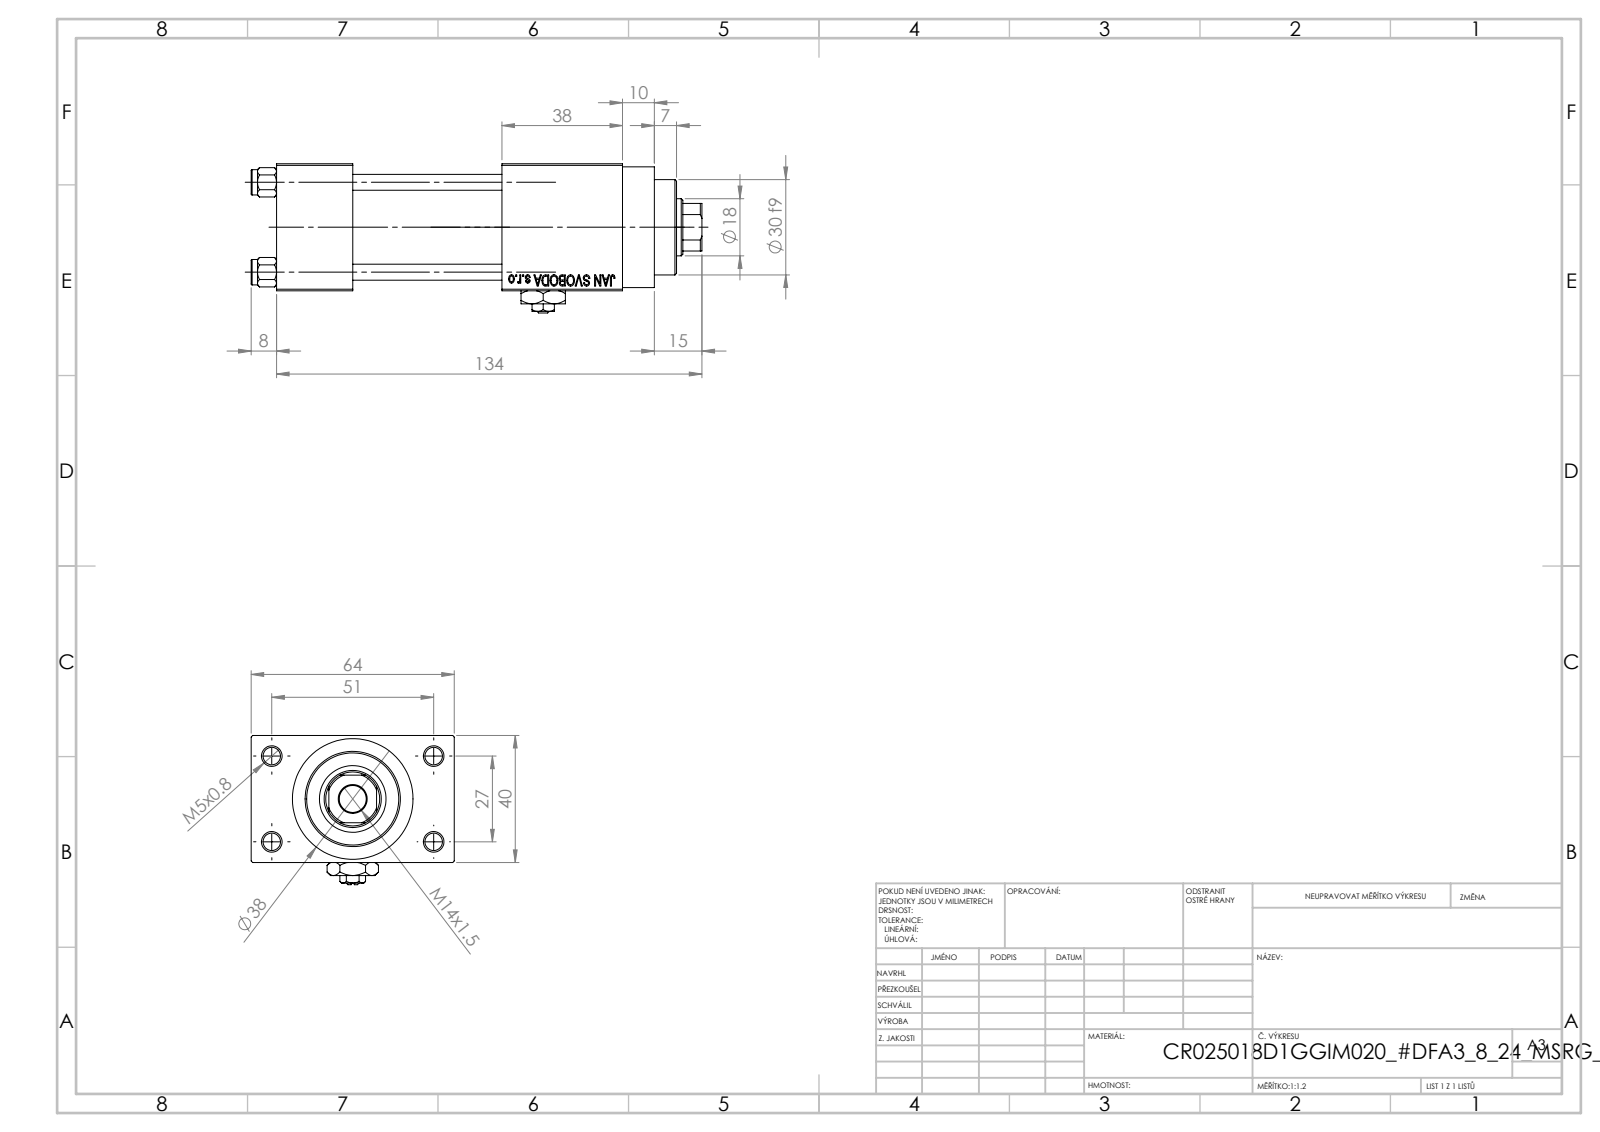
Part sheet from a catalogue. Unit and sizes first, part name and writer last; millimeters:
Units: millimetres
Overall size (bounding box): 142 × 64 × 47
Round holes (diameter × count): ⌀5 ×4, ⌀5.5 ×4, ⌀20 ×3, ⌀7 ×2, ⌀13.16 ×2, ⌀8.5 ×1, ⌀18 ×1, ⌀21 ×1, ⌀25 ×1, ⌀30 ×1
Round bosses / shafts (diameter × count): ⌀8 ×4, ⌀38 ×1, ⌀31 ×1
Partial cylindrical surfaces — rounded edges, fillets, slot ends (radius × count): R8.5 ×1
Main face-to-face distances: 40, 12, 52, 47, 24, 71, 64, 38, 85, 109
Hole centre spacings: 11.37, 20.01, 28.3, 28.85, 29.89, 39.66, 48.34, 27
Volume: 180 837 mm³ · Surface area: 64 776 mm²
Bodies: 12 solids, 1147 faces (518 planar, 91 cylindrical, 538 other)
Part name (STEP PRODUCT): V215CR_VCP_D; Zatka_pro_OIL_PORT; V215CR_D_Body; V215CR_D_TYCINKA (+2 more)
STEP written by: SolidWorks 2019 (CONFIG_CONTROL_DESIGN)
